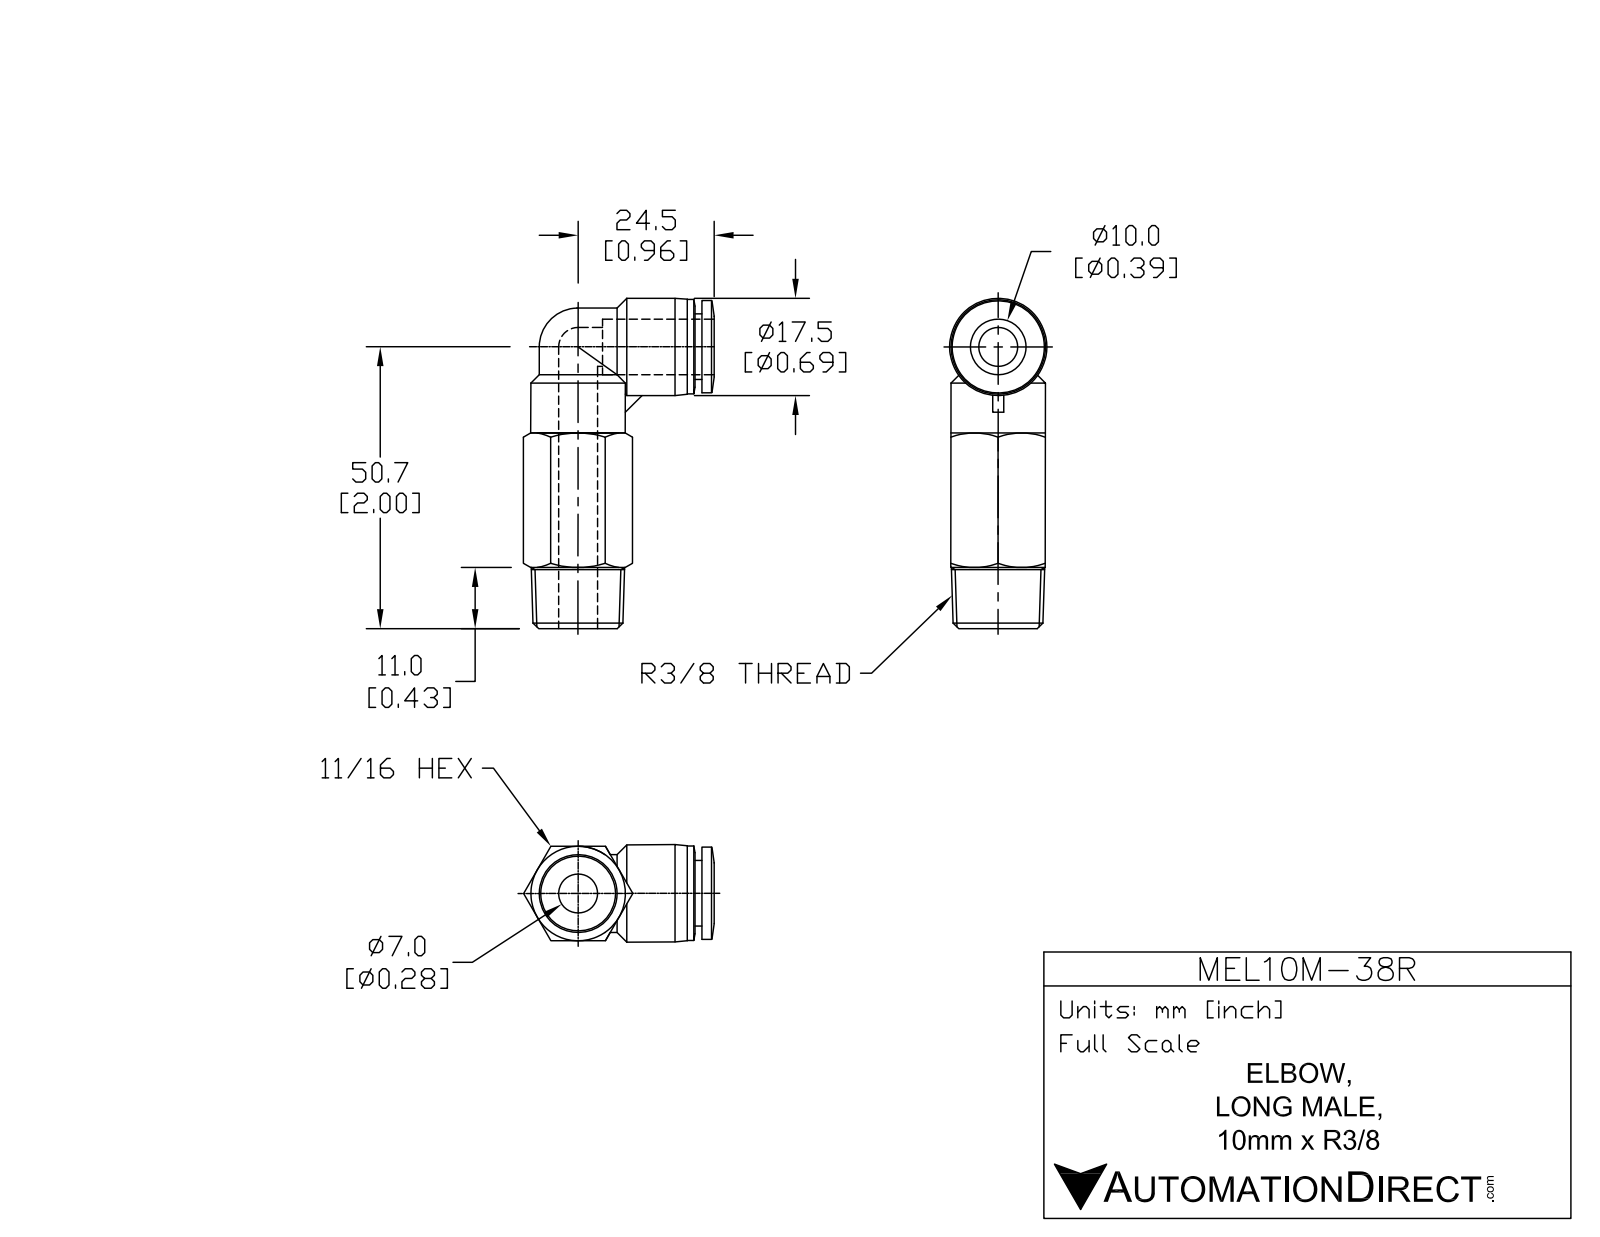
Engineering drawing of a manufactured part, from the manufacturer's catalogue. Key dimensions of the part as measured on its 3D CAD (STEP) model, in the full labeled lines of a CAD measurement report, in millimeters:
Part name (STEP PRODUCT): MEL10M-38R
STEP written by: SolidWorks 2015 (AUTOMOTIVE_DESIGN)
Units: millimetres
Bodies: 1 solid, 70 faces (16 planar, 20 cylindrical, 34 other)
Overall size (bounding box): 59.5 × 34.4 × 17.5
Volume: 12 500 mm³ · Surface area: 6 386 mm²
Round holes (diameter × count): ⌀7 ×2, ⌀10.3 ×1
Round bosses / shafts (diameter × count): ⌀17 ×2, ⌀17.5 ×1, ⌀16.6 ×1, ⌀14 ×1, ⌀11.8 ×1
Partial cylindrical surfaces — rounded edges, fillets, slot ends (radius × count): R7 ×1
Main face-to-face distances: 17, 1.2, 16.7, 18, 7.5, 9.5, 11, 2, 15.3, 1.4
